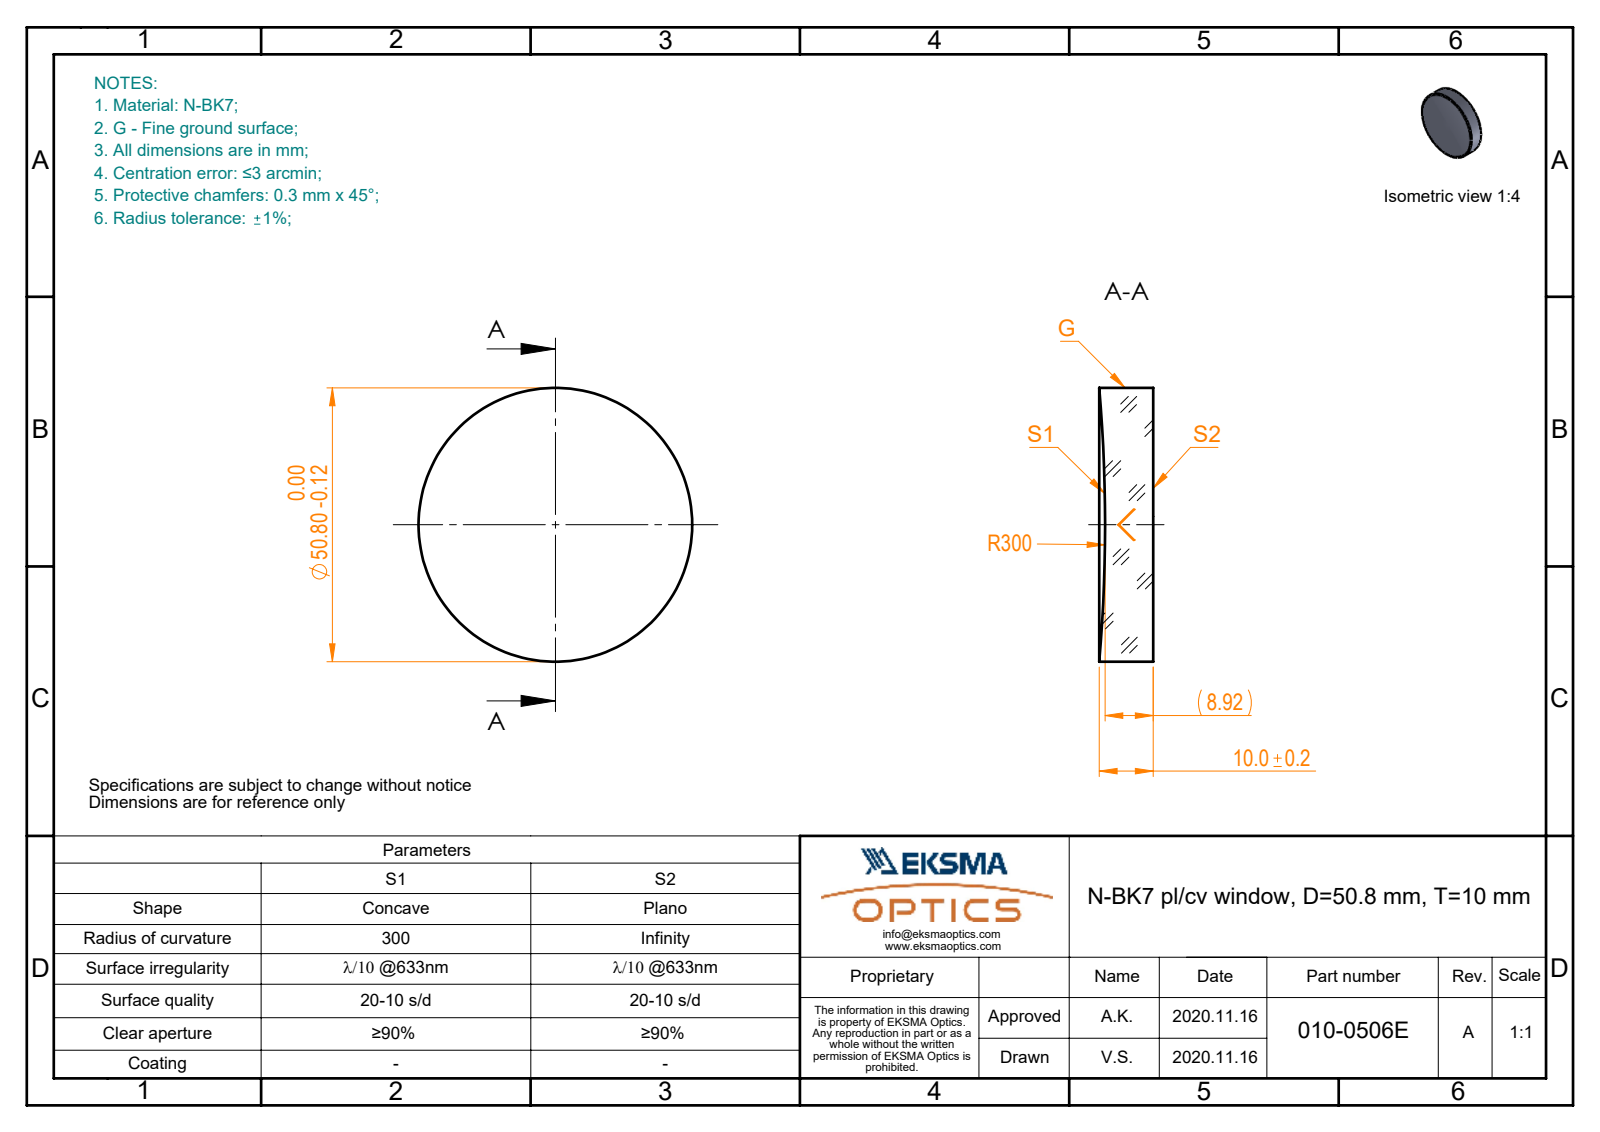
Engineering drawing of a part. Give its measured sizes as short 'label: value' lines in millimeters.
name: 010-0506E_N-BK7_PCV_window
written by: SolidWorks 2019 (CONFIG_CONTROL_DESIGN)
unit: mm
bodies: 1 solid, 5 faces (1 planar, 2 cylindrical, 2 other)
size: 50.8 × 50.8 × 10
volume: 19 176 mm³; area: 5 653 mm²
bosses: 1× ⌀50.8
